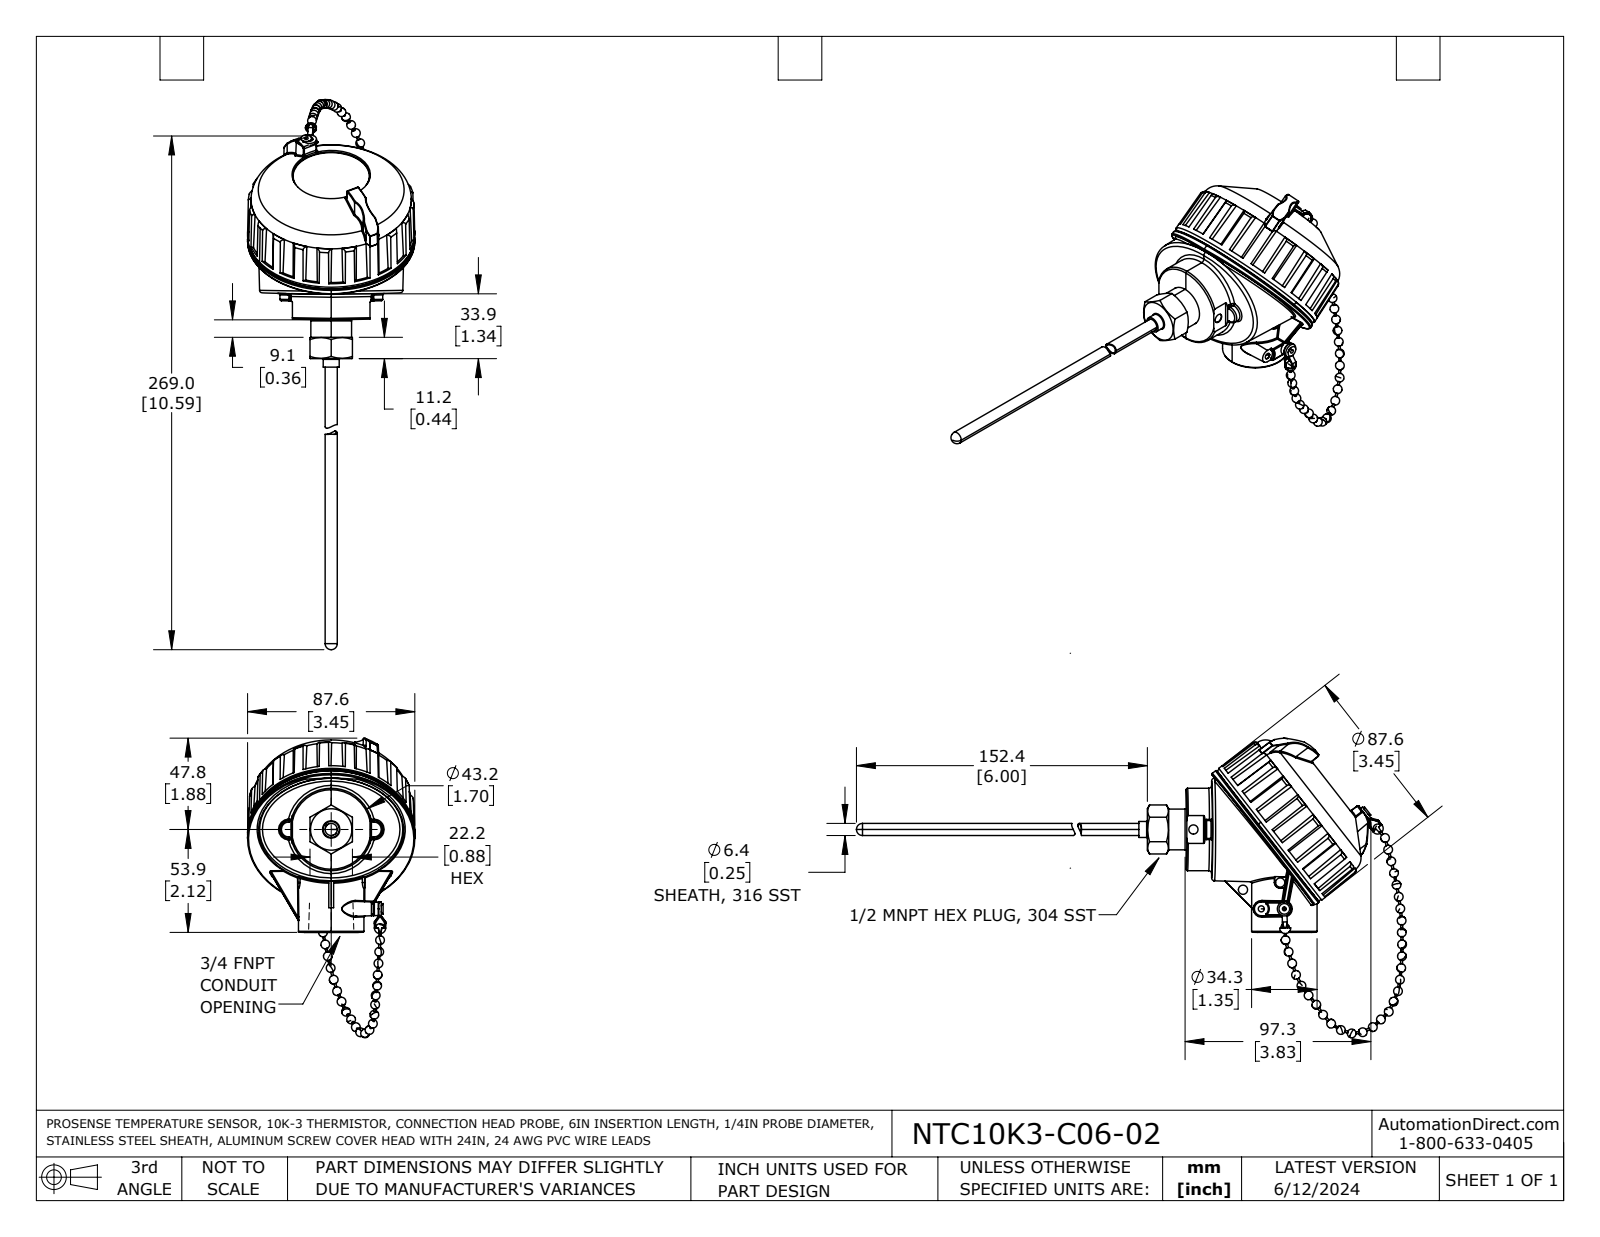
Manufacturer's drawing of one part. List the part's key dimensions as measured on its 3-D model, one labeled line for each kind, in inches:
Part name (STEP PRODUCT): NTC10K3-C06-02
STEP written by: SolidWorks 2021 (AUTOMOTIVE_DESIGN)
Units: inches
Bodies: 10 solids, 962 faces (232 planar, 189 cylindrical, 541 other)
Overall size (bounding box): 11.339 × 6.177 × 3.45
Volume: 9.074 in³ · Surface area: 121.4 in²
Round holes (diameter × count): ⌀0.19 ×3, ⌀0.08 ×2, ⌀0.144 ×2, ⌀0.125 ×1, ⌀0.165 ×1, ⌀0.21 ×1, ⌀0.253 ×1, ⌀0.438 ×1, ⌀0.891 ×1, ⌀3.005 ×1, ⌀3.028 ×1, ⌀3.15 ×1
Round bosses / shafts (diameter × count): ⌀0.04 ×31, ⌀0.29 ×2, ⌀0.123 ×2, ⌀3.45 ×1, ⌀3.405 ×1, ⌀3.122 ×1, ⌀2.994 ×1, ⌀1.7 ×1
Partial cylindrical surfaces — rounded edges, fillets, slot ends (radius × count): R0.02 ×21, R0.03 ×11, R0.015 ×6, R0.06 ×5, R0.185 ×2, R0.064 ×1, R0.145 ×1
Main face-to-face distances: 1.483, 1.42, 0.063, 0.14, 1.56, 1.623, 0.525, 1.561, 1.42, 0.062
Hole centre spacings: 0.07, 0.475, 0.546, 0.549, 0.668, 0.782, 0.939, 0.983
